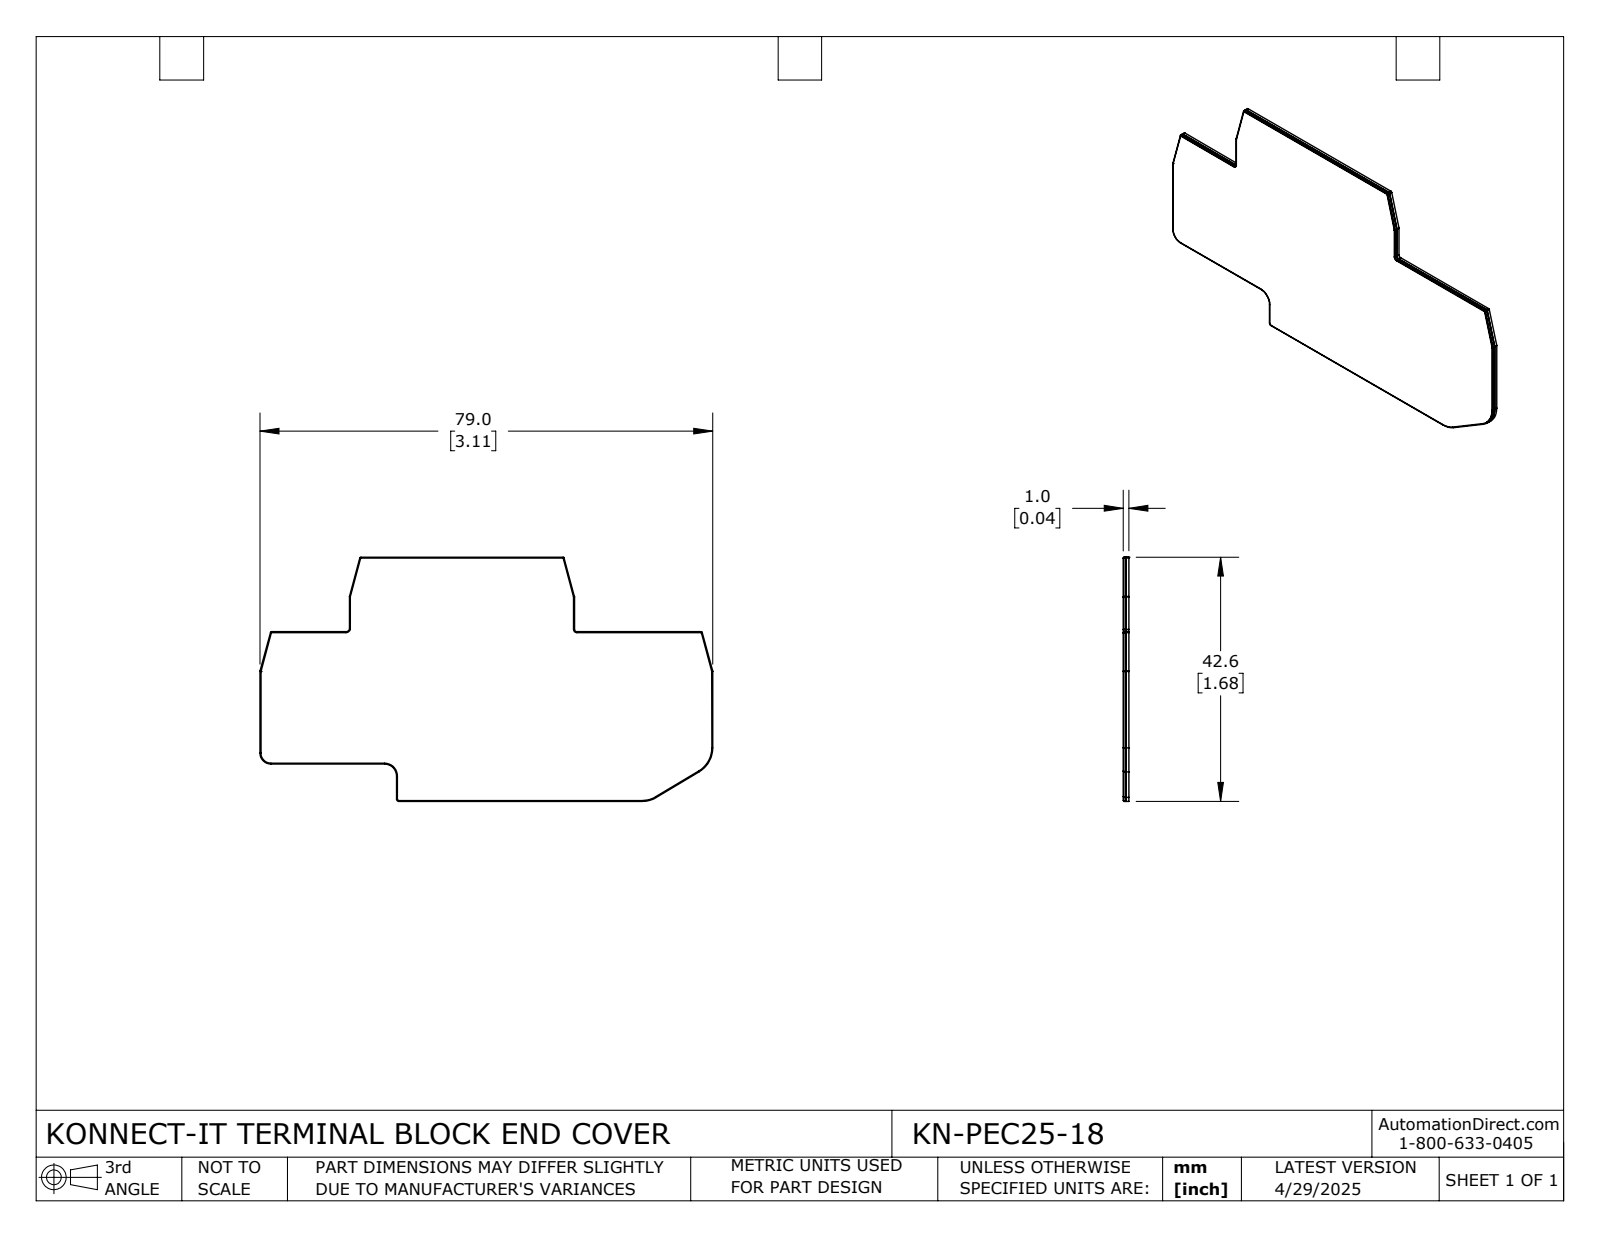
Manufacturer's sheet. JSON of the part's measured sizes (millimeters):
{"part_name": "KN-PEC25-18", "step_written_by": "SolidWorks 2024 (CONFIG_CONTROL_DESIGN)", "units": "millimeters", "bodies": {"solids": 2, "faces": 95, "planar": 50, "cylindrical": 45, "other": 0}, "overall_size": [79.04, 42.62, 1], "volume_mm3": 2630, "surface_area_mm2": 10763, "partial_cylinders_radius": [[0.2, 8], [0.4, 2], [4.75, 2], [4.9, 2], [0.25, 1], [0.55, 1], [0.6, 1], [0.75, 1]], "face_to_face_distances": [0.5, 1, 13.01, 0.9, 0.4, 42.62, 29.61, 6.51, 23.1, 36.11]}
